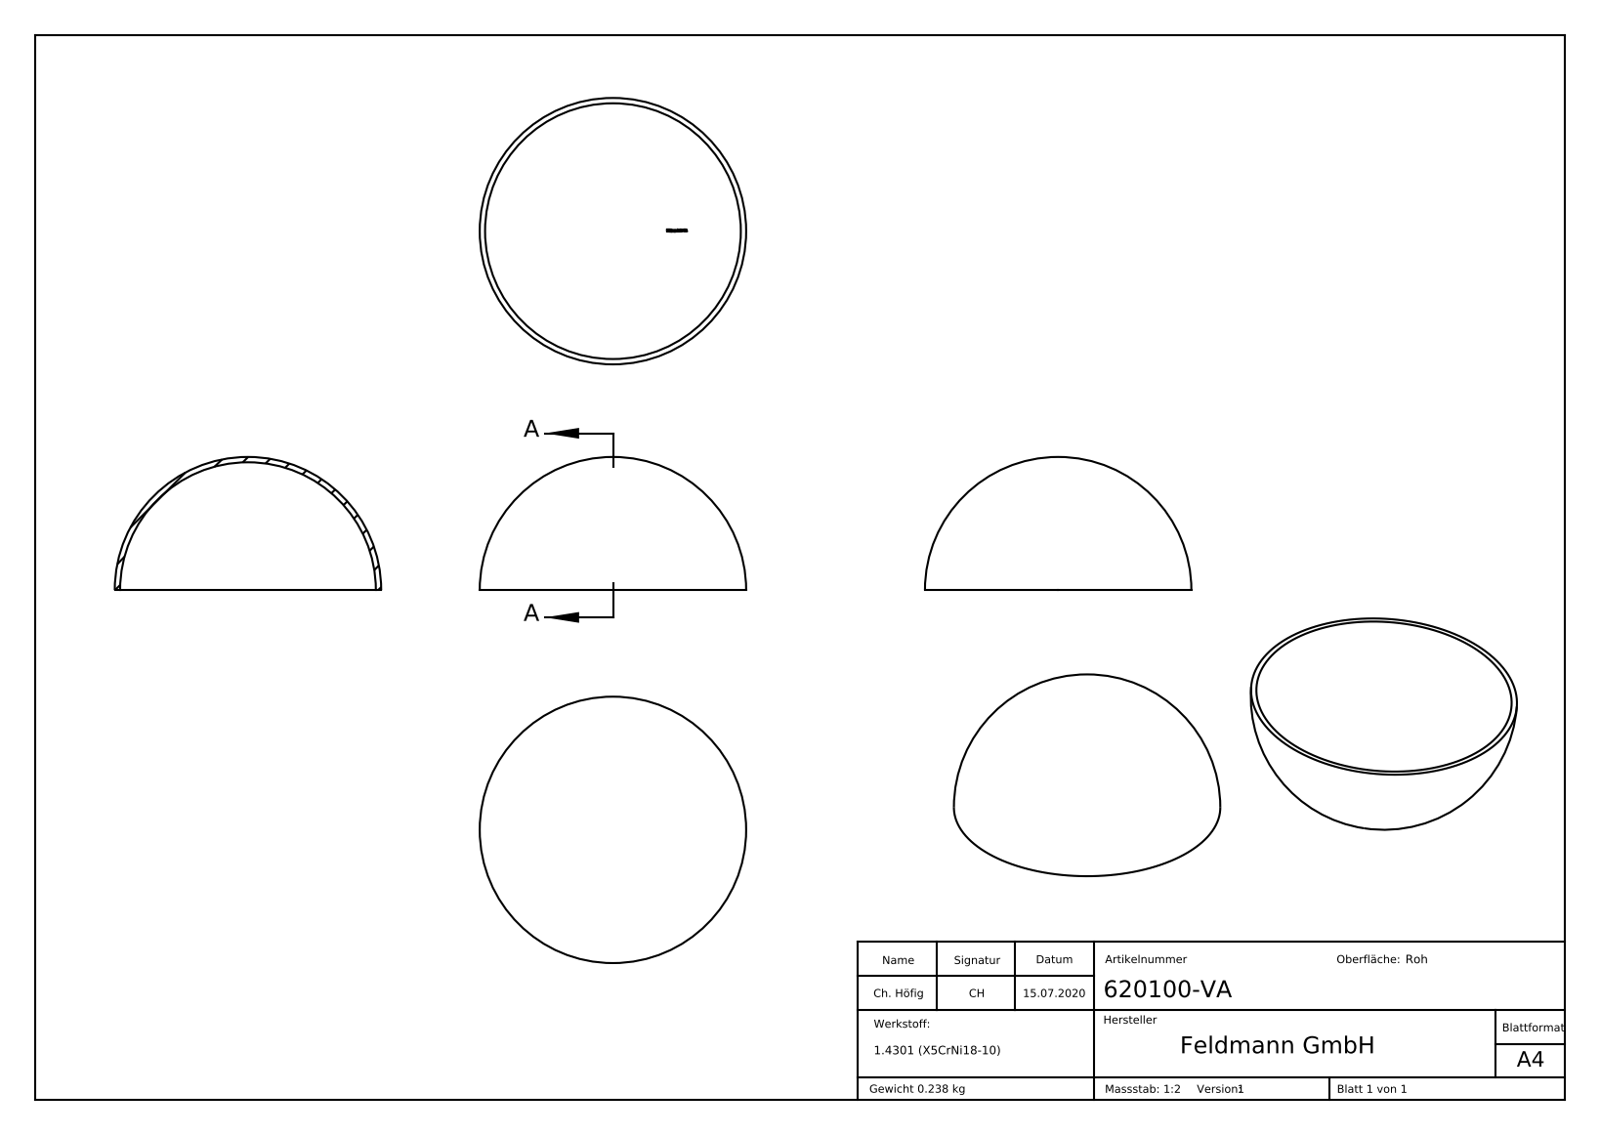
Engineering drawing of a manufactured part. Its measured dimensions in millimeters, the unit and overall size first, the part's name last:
Units: millimetres
Overall size (bounding box): 100 × 100 × 50
Main face-to-face distances: 0.45, 5.1, 0.53, 3.79, 0.61, 1.19, 0.55, 0.5, 0.81, 1.31
Volume: 30 176 mm³ · Surface area: 30 805 mm²
Bodies: 1 solid, 209 faces (92 planar, 0 cylindrical, 117 other)
Part name (STEP PRODUCT): 620100-VA
STEP written by: SolidWorks 2018 (CONFIG_CONTROL_DESIGN)
